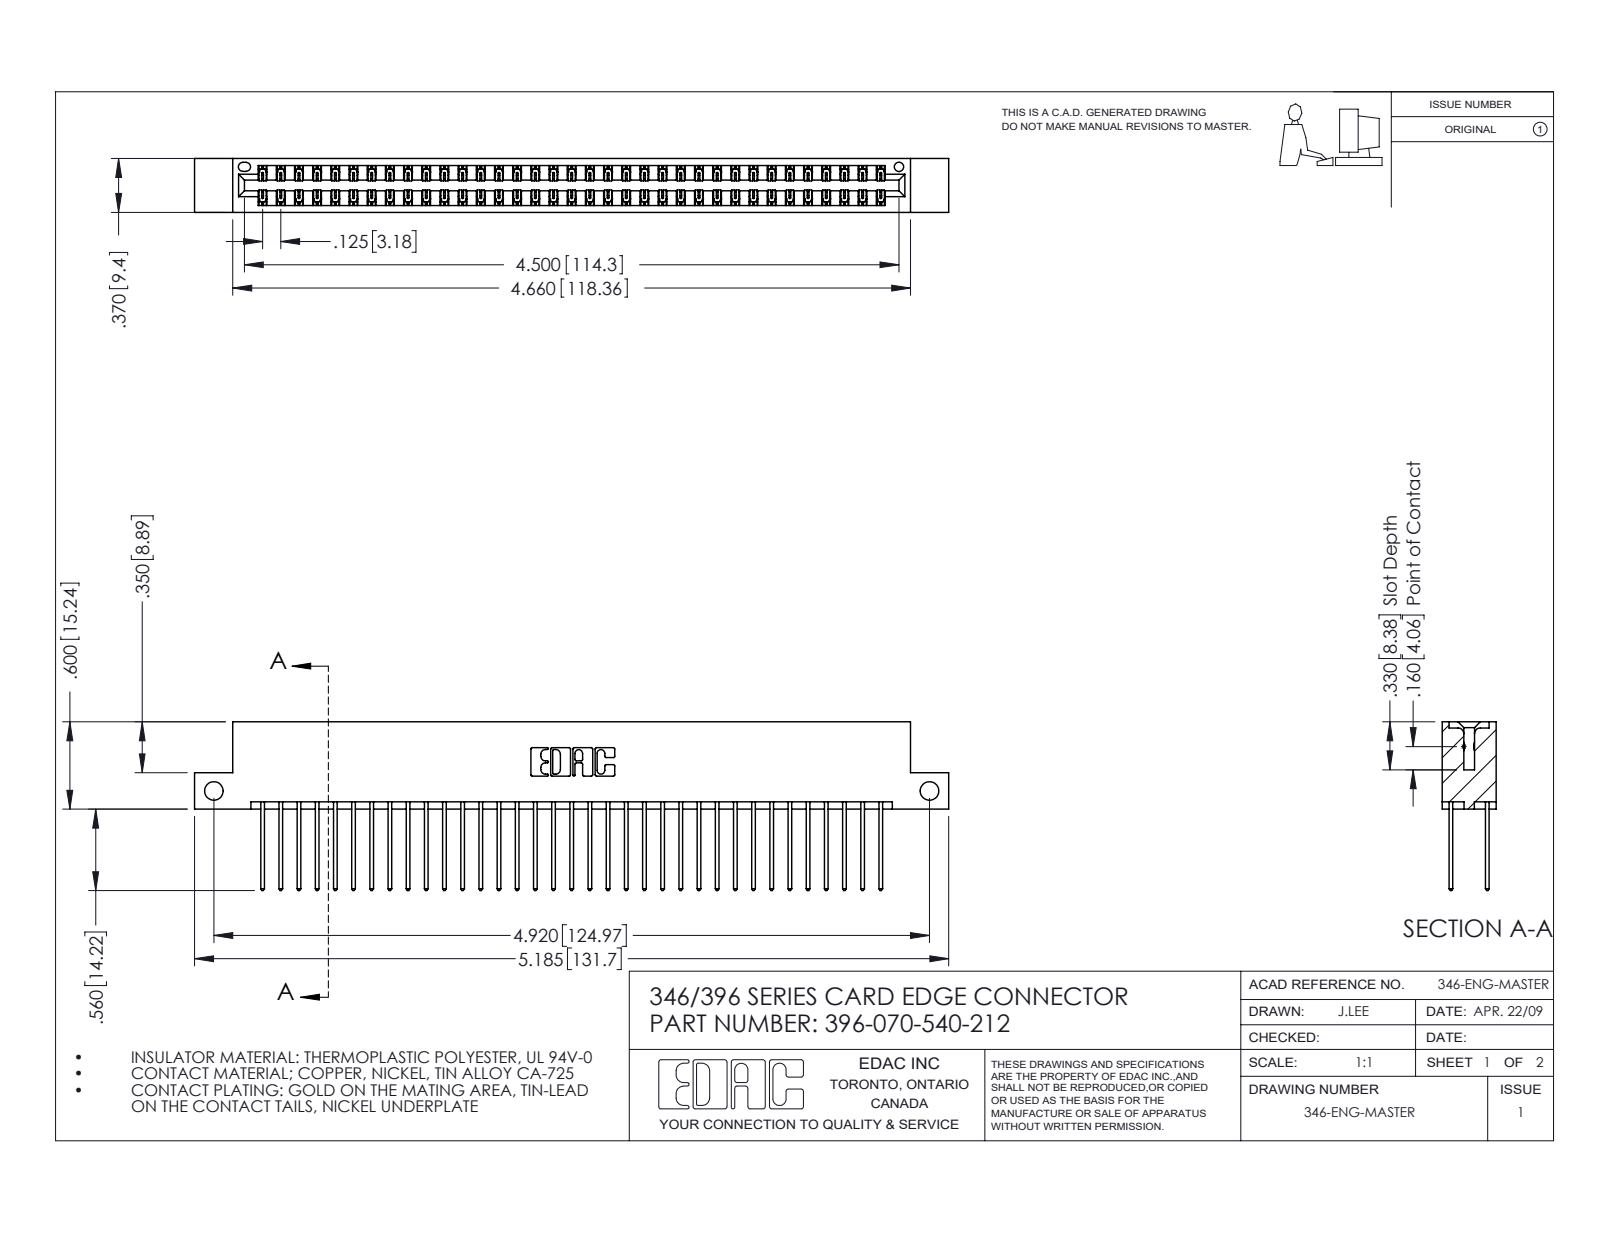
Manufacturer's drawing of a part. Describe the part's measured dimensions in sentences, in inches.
The part is named "346 Part_Flush Mounting Lugs - Side Mount; 396-070-540-212; 345-292-001_345-293-140". Its 3-D file was written by "SolidWorks 2016 (CONFIG_CONTROL_DESIGN)". It is 71 solids with 3762 faces: 2526 planar, 1236 cylindrical and 0 other. Overall it measures 5.185 by 1.16 by 0.37 inches. Its volume is 0.791 cubic inches and its surface area 29.19 square inches. Round holes: 2 of diameter 0.128, 1 of diameter 0.064. Partial cylindrical surfaces (rounded edges, fillets, slot ends): 105 of radius 0.006, 70 of radius 0.01, 22 of radius 0.01, 6 of radius 0.007, 6 of radius 0.031, 3 of radius 0.026, 2 of radius 0.014, 2 of radius 0.022. The main face-to-face distances are 0.048, 0.322, 0.25, 0.072, 0.298, 0.025, 0.37, 0.275, 0.148, 0.222. The hole center spacings are 4.92.
